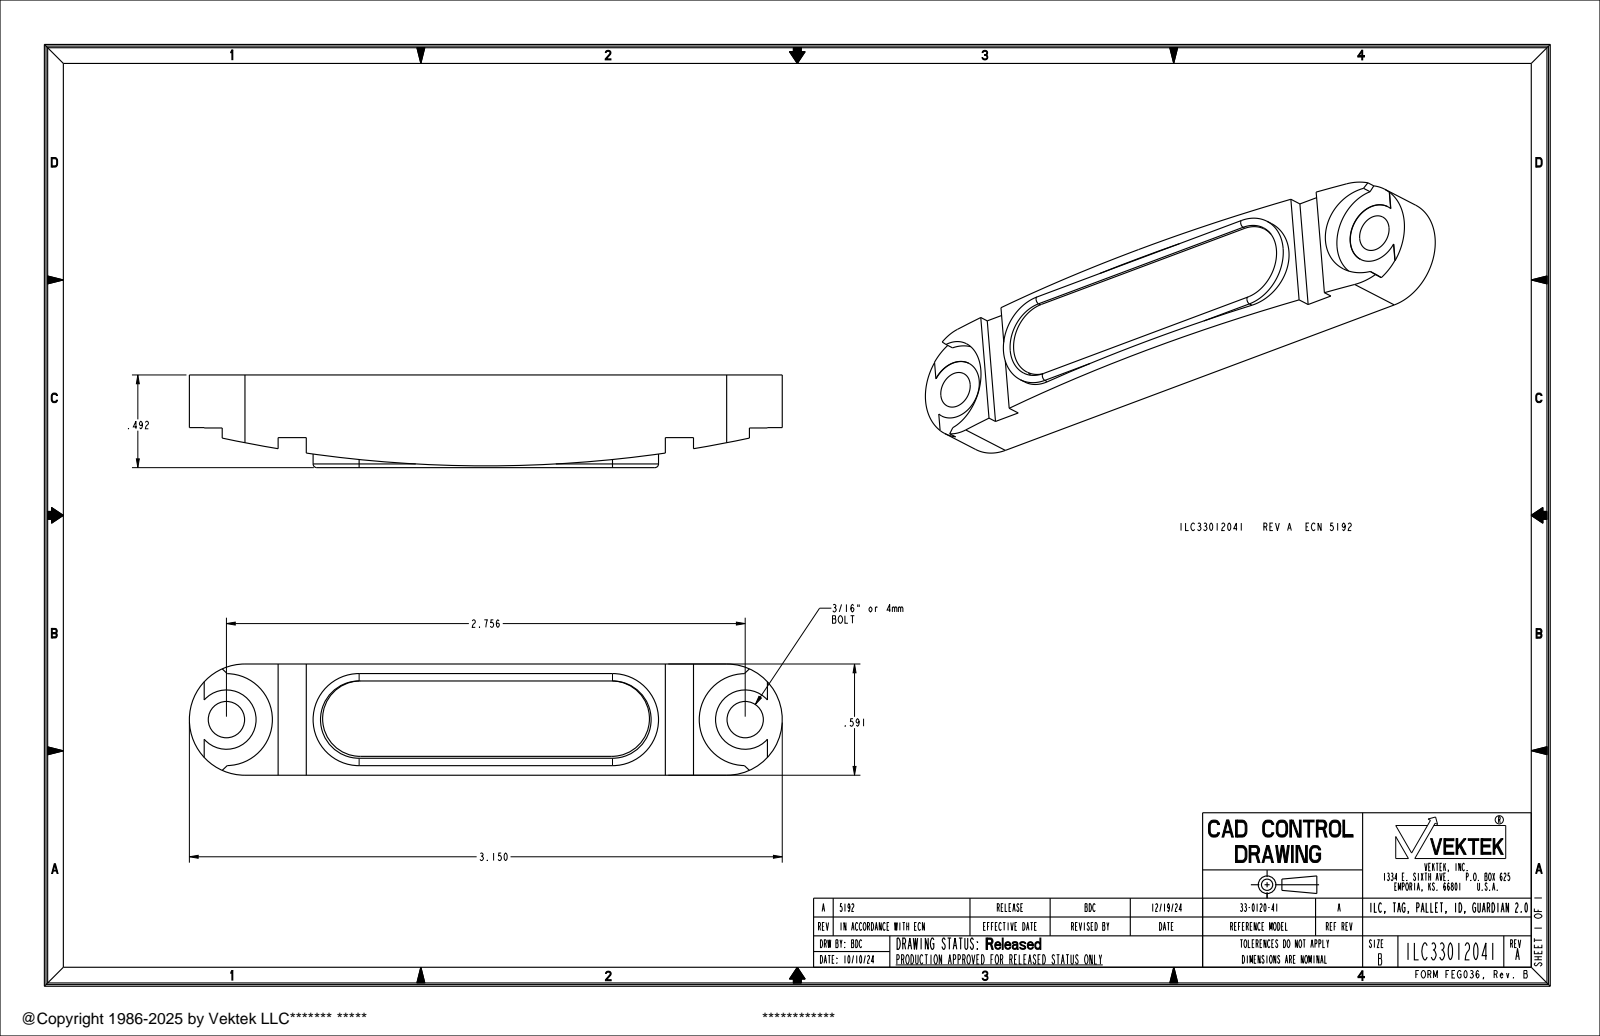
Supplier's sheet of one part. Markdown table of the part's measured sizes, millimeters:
| quantity | value |
| --- | --- |
| part name | ILC33012041 |
| STEP written by | CREO PARAMETRIC BY PTC INC, 2021164 (AUTOMOTIVE_DESIGN) |
| units | millimeters |
| bodies | 1 solid, 56 faces (33 planar, 21 cylindrical, 2 other) |
| overall size | 80 × 15 × 12.5 |
| volume | 10 500 mm³ |
| surface area | 5 709 mm² |
| round holes (diameter × count) | 4.9 × 2 |
| partial cylindrical surfaces (radius × count) | 0.5 × 2, 4 × 2, 5.1 × 2, 5.2 × 2, 6.2 × 2, 6.2 × 2, 7.5 × 2, 170.7 × 1 |
| main face-to-face distances | 15, 9, 2.5, 11.5, 11.6, 2.5, 2.3, 12.7, 8.5, 0.6 |
| hole center spacings | 70 |
